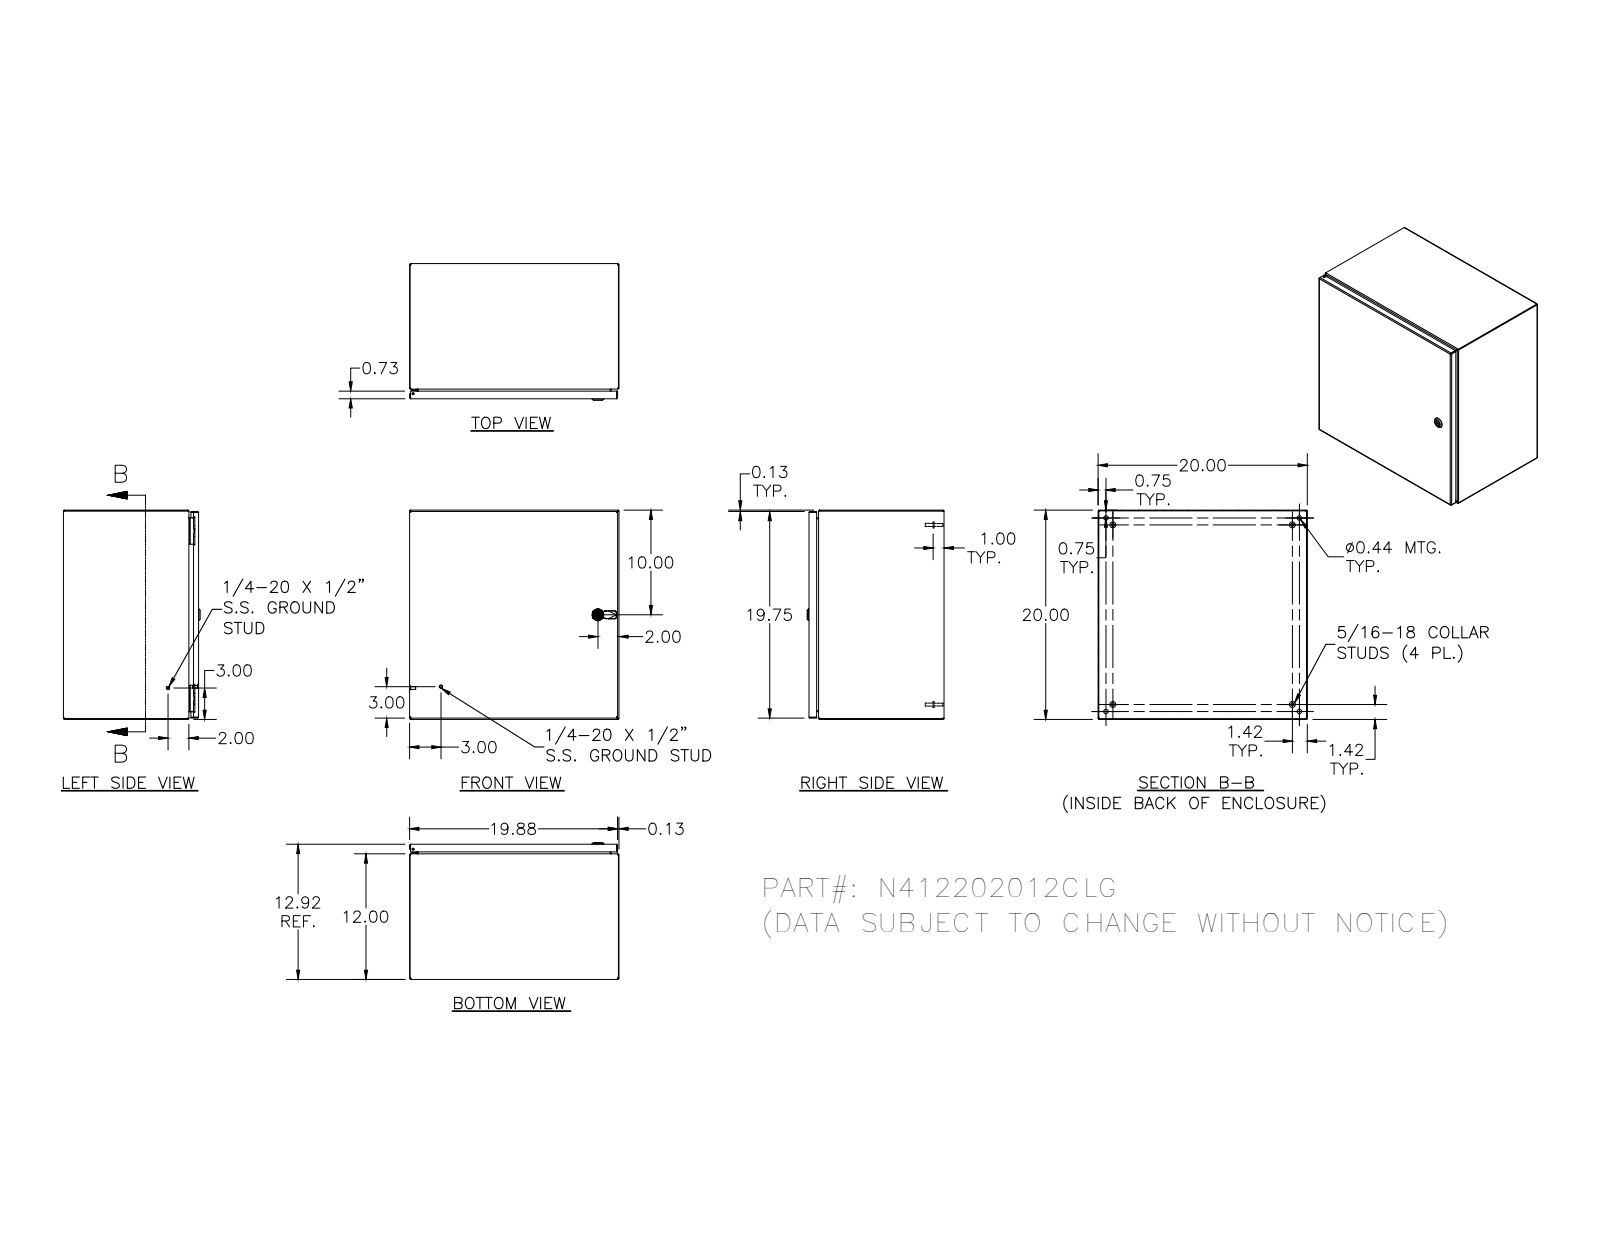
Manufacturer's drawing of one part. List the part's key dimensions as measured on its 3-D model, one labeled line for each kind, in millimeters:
Part name (STEP PRODUCT): N412202012CLG
STEP written by: SolidWorks 2018 (AUTOMOTIVE_DESIGN)
Units: millimetres
Bodies: 33 solids, 1449 faces (530 planar, 547 cylindrical, 372 other)
Overall size (bounding box): 508 × 508 × 332.1
Volume: 2 330 000 mm³ · Surface area: 2 492 000 mm²
Round holes (diameter × count): ⌀4.8 ×5, ⌀2.4 ×4, ⌀3.9 ×4, ⌀4.2 ×4, ⌀4.4 ×4, ⌀11.1 ×4, ⌀4 ×2, ⌀4.7 ×1, ⌀5 ×1, ⌀8 ×1, ⌀10 ×1, ⌀10.2 ×1
Round bosses / shafts (diameter × count): ⌀6.4 ×10, ⌀14.3 ×4, ⌀9.1 ×4, ⌀8.1 ×4, ⌀7.6 ×4, ⌀7 ×4, ⌀6.5 ×4, ⌀4.2 ×4
Partial cylindrical surfaces — rounded edges, fillets, slot ends (radius × count): R0.3 ×30, R0.8 ×30, R1.3 ×26, R2.7 ×20, R0.4 ×18, R3.2 ×16, R0.5 ×13, R0.8 ×8
Main face-to-face distances: 1.9, 326.2, 506.1, 504.2, 1.9, 506.1, 508, 324.3, 328.1, 23.3
Hole centre spacings: 406.4, 16.8, 16.7, 33.2, 49.9, 389.6, 406.3, 423.1
